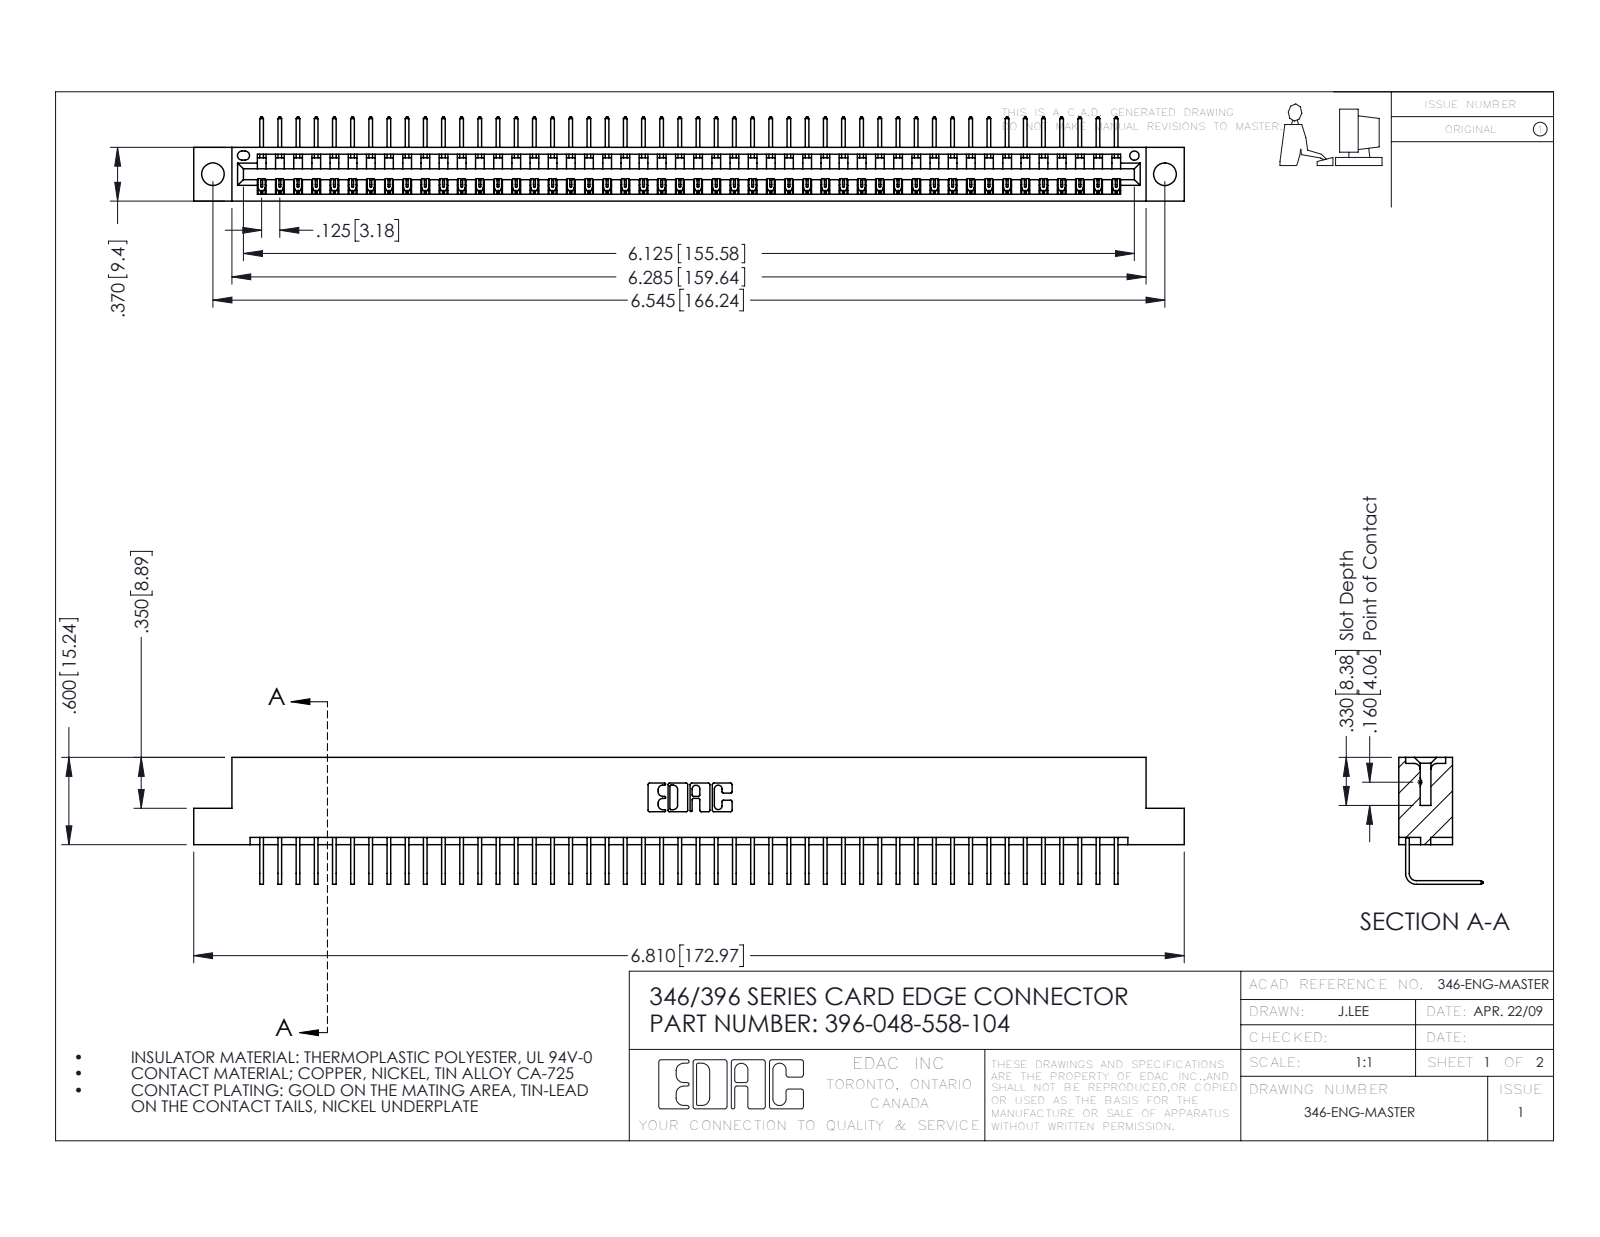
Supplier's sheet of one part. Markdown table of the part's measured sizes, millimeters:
| quantity | value |
| --- | --- |
| part name | 396-048-558-104; 345-292-001_558 Tail - 2; 346 Part_Flush Mounting Lugs - 0.156 Dia-TH |
| STEP written by | SolidWorks 2016 (CONFIG_CONTROL_DESIGN) |
| units | millimeters |
| bodies | 49 solids, 3002 faces (2092 planar, 910 cylindrical, 0 other) |
| overall size | 173 × 22.2 × 14.7 |
| volume | 16 670 mm³ |
| surface area | 21 660 mm² |
| round holes (diameter × count) | 4 × 2, 1.6 × 1 |
| partial cylindrical surfaces (radius × count) | 0.2 × 96, 0.3 × 22, 0.2 × 6, 0.8 × 6, 0.7 × 3, 0.8 × 2, 1 × 2, 0.4 × 1 |
| main face-to-face distances | 8.2, 1.2, 9.4, 6.4, 7.6, 0.6, 1.8, 3.8, 5.6, 2.5 |
| hole center spacings | 6.2, 160.9, 166.2 |
